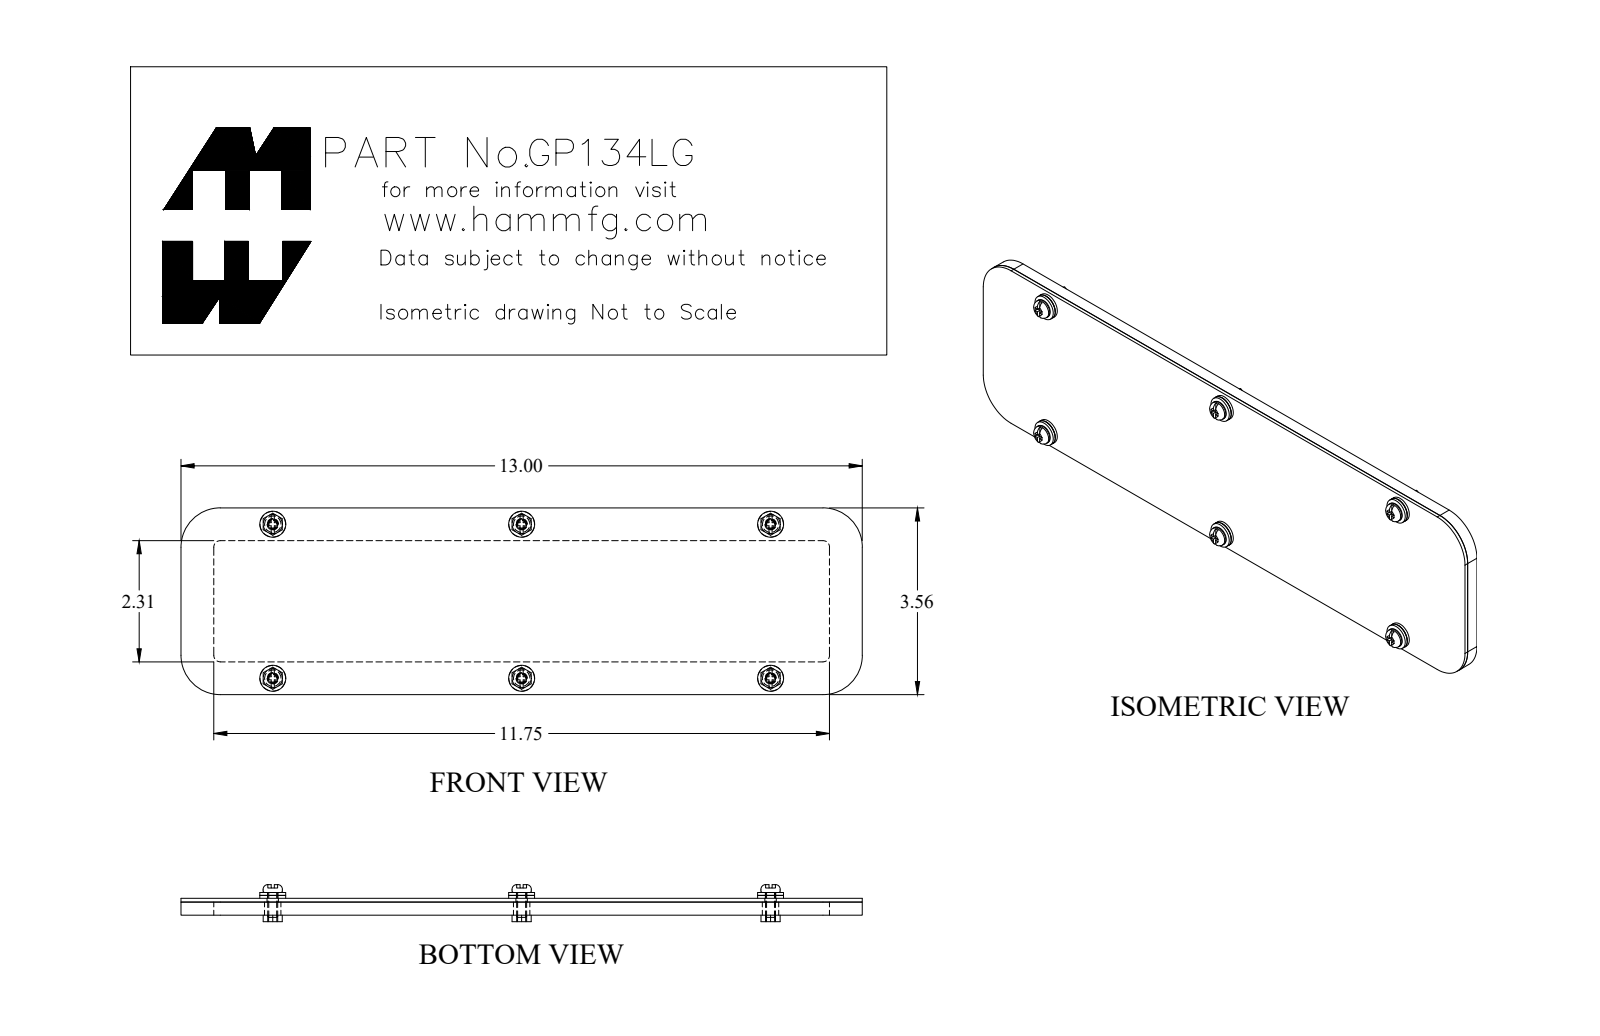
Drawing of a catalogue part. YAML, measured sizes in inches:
part_name: "GP134LG"
step_written_by: "SolidWorks 2018 (AUTOMOTIVE_DESIGN)"
units: inches
bodies: {solids: 20, faces: 346, planar: 190, cylindrical: 120, other: 36}
overall_size: [13, 3.562, 0.707]
volume: 8.167
surface_area: 156.4
round_holes:
  - {diameter: 0.156, count: 6}
  - {diameter: 0.197, count: 6}
  - {diameter: 0.218, count: 6}
  - {diameter: 0.313, count: 6}
round_bosses_or_shafts:
  - {diameter: 0.494, count: 6}
  - {diameter: 0.488, count: 6}
  - {diameter: 0.367, count: 6}
  - {diameter: 0.19, count: 6}
partial_cylinders:
  - {radius: 0.125, count: 4}
  - {radius: 0.75, count: 4}
face_to_face_distances: [0.072, 0.322, 0.25, 0.625, 2.937, 3.562, 2.312, 0.11, 0.182, 0.432]
hole_center_spacings: [4.75, 5.585, 9.5, 9.944, 2.937, 5.585, 2.937, 2.937]
